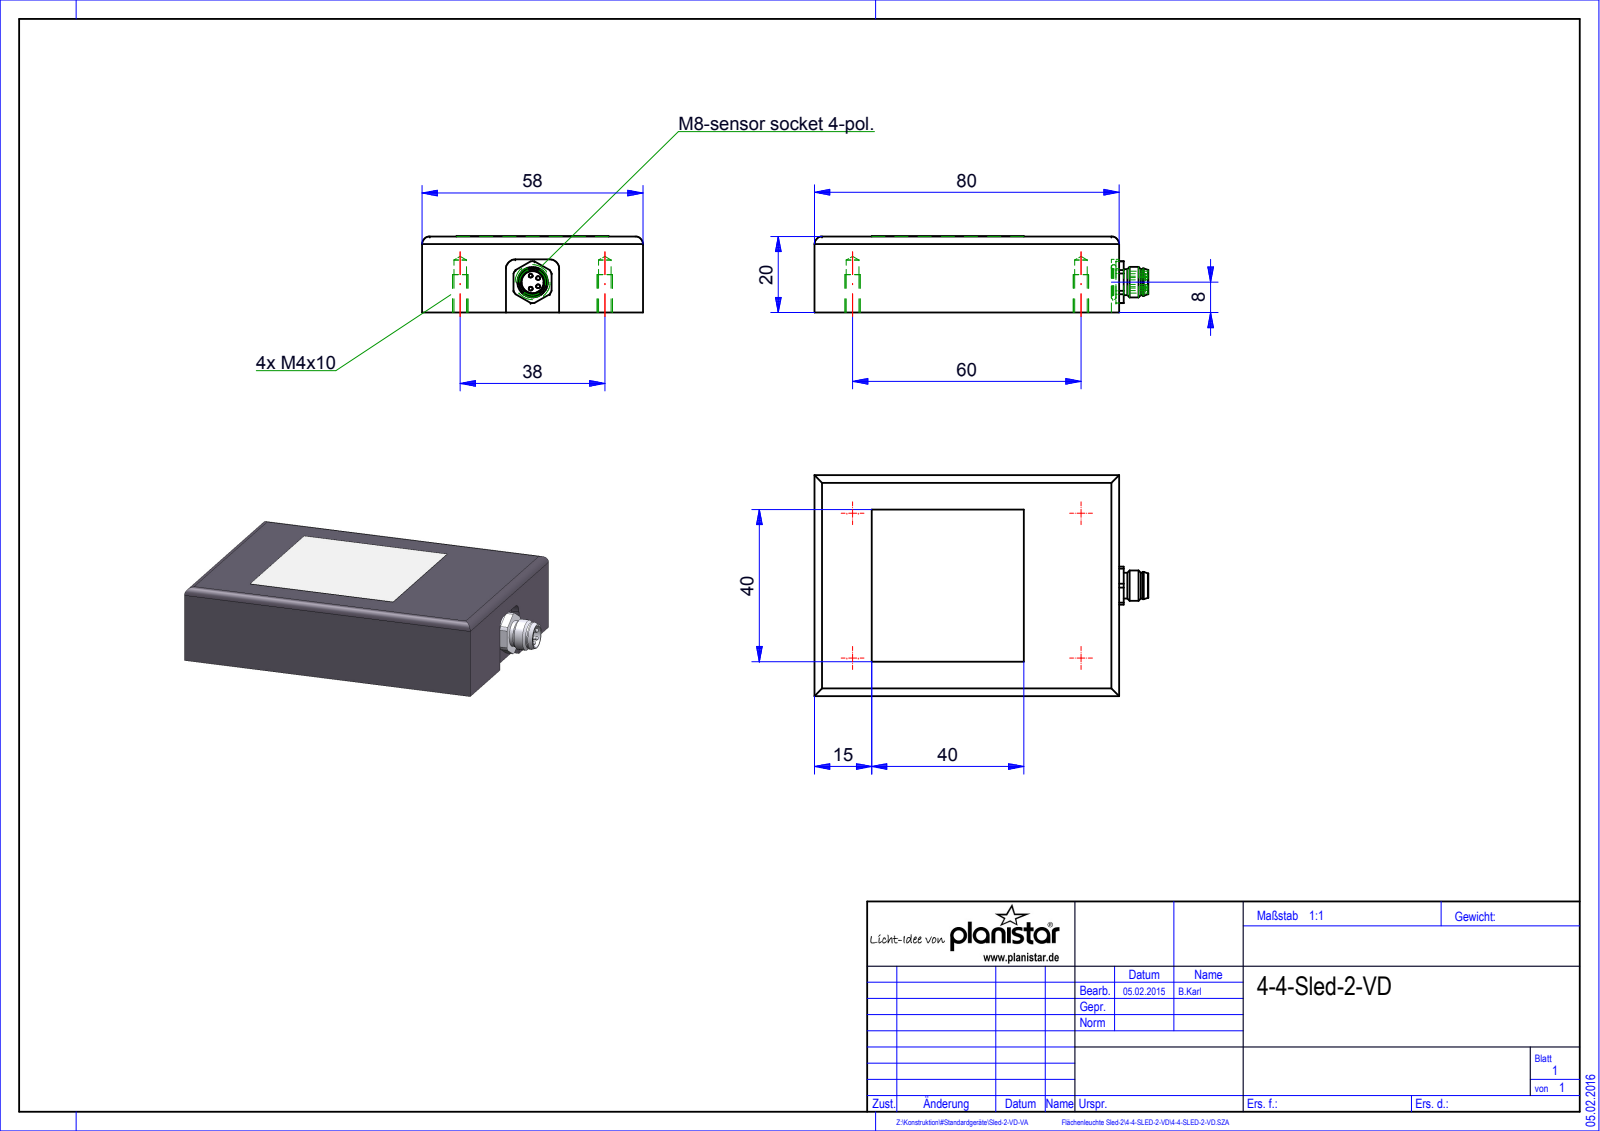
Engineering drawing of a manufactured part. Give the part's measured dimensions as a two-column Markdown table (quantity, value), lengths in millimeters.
| quantity | value |
| --- | --- |
| part name | Root; Baugruppe_Xled-2-VD; QUADER_0; 09-3391-00-04 |
| STEP written by | HiCAD 2015 2002.1 Build 408 (CONFIG_CONTROL_DESIGN) |
| units | millimeters |
| bodies | 2 solids, 75 faces (31 planar, 31 cylindrical, 13 other) |
| overall size | 87.7 × 58 × 20.1 |
| volume | 92 101 mm³ |
| surface area | 15 923 mm² |
| round holes (diameter × count) | 3.3 × 4, 4 × 4, 5.8 × 1 |
| round bosses / shafts (diameter × count) | 1 × 4, 8 × 1, 7.2 × 1, 6.8 × 1, 6.4 × 1 |
| partial cylindrical surfaces (radius × count) | 2 × 4, 2.5 × 2, 5.5 × 1 |
| main face-to-face distances | 20, 20.1, 58, 80, 2, 78, 1.2, 10, 81.2, 3.2 |
| hole center spacings | 38, 60, 71.02 |
